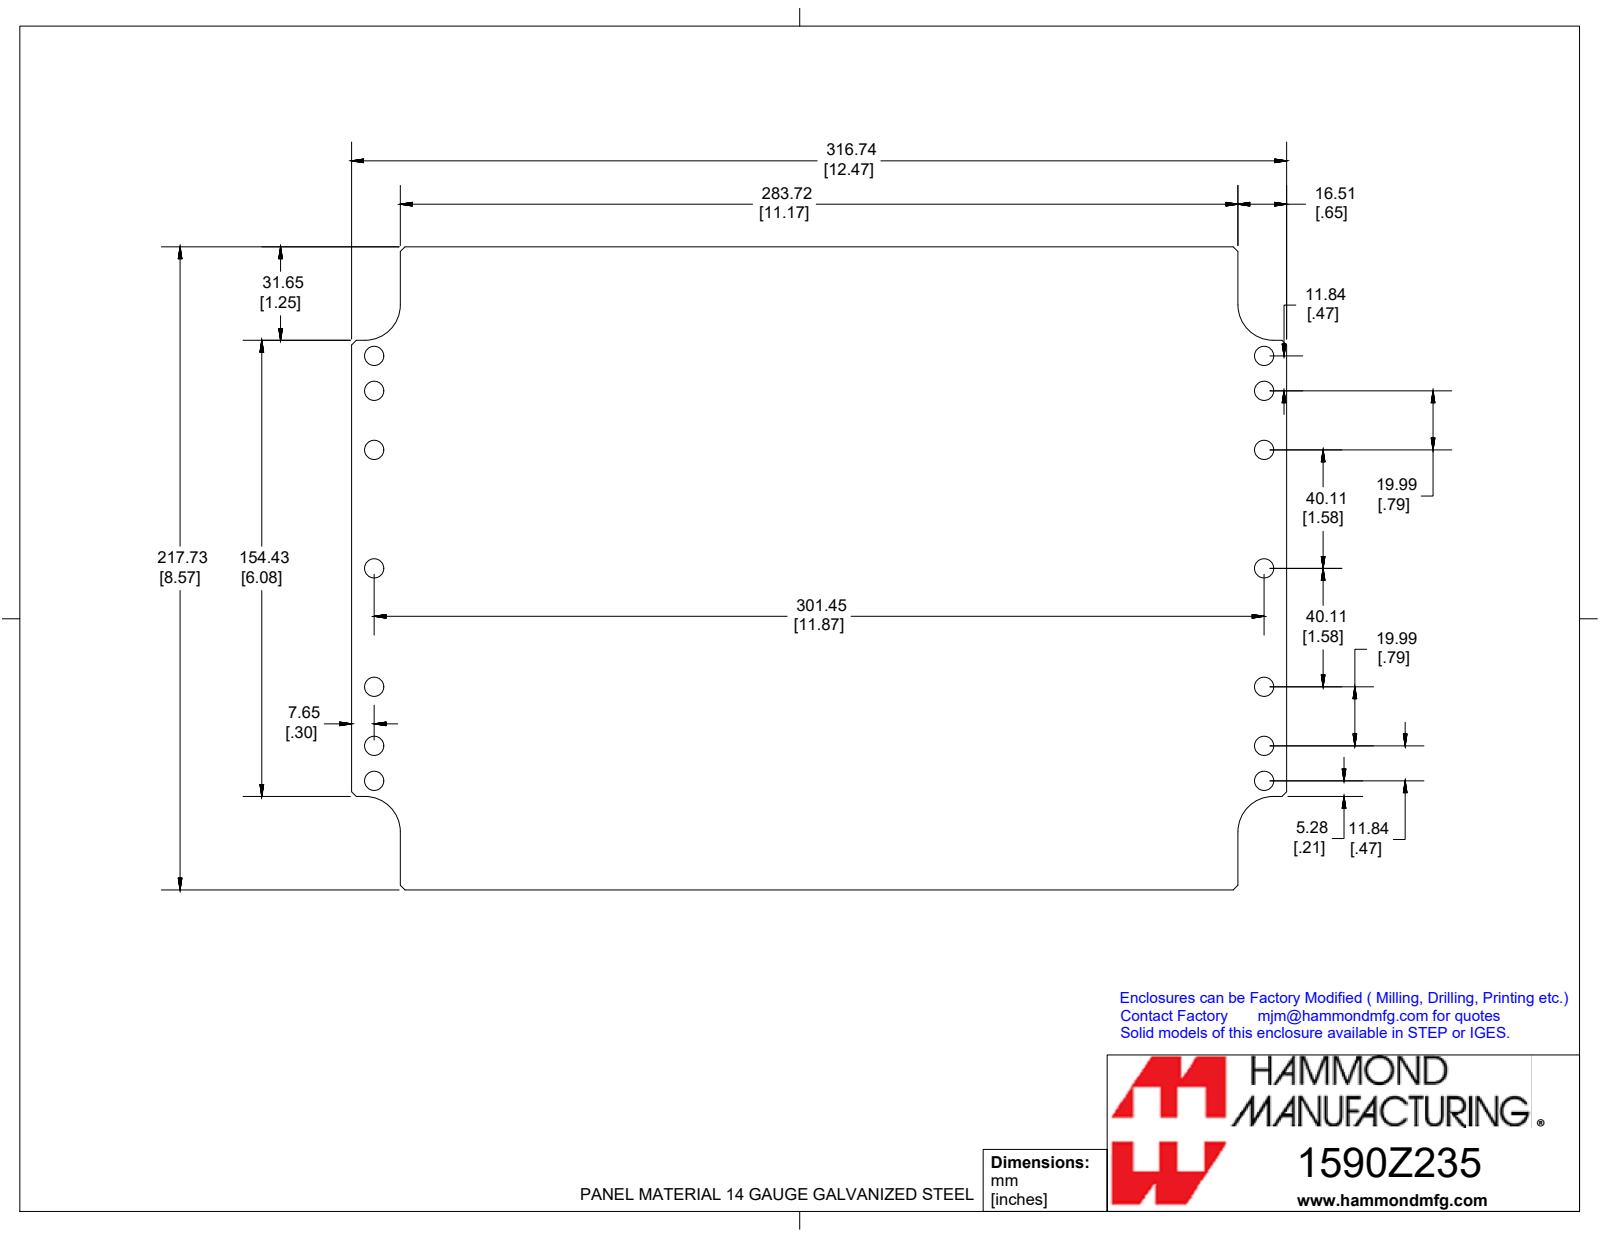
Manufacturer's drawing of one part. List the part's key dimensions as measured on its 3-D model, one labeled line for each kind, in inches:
Part name (STEP PRODUCT): 1590Z235PL
STEP written by: SolidWorks 2019 (CONFIG_CONTROL_DESIGN)
Units: inches
Bodies: 1 solid, 40 faces (22 planar, 18 cylindrical, 0 other)
Overall size (bounding box): 12.47 × 8.572 × 0.064
Volume: 6.538 in³ · Surface area: 209.3 in²
Round holes (diameter × count): ⌀0.281 ×14
Partial cylindrical surfaces — rounded edges, fillets, slot ends (radius × count): R0.472 ×4
Main face-to-face distances: 0.063, 8.572, 12.47, 0.65, 11.82, 11.17, 1.246, 7.326, 0.421, 13.448
Hole centre spacings: 11.85, 0.466, 0.787, 1.253, 1.579, 2.366, 2.832, 3.945
